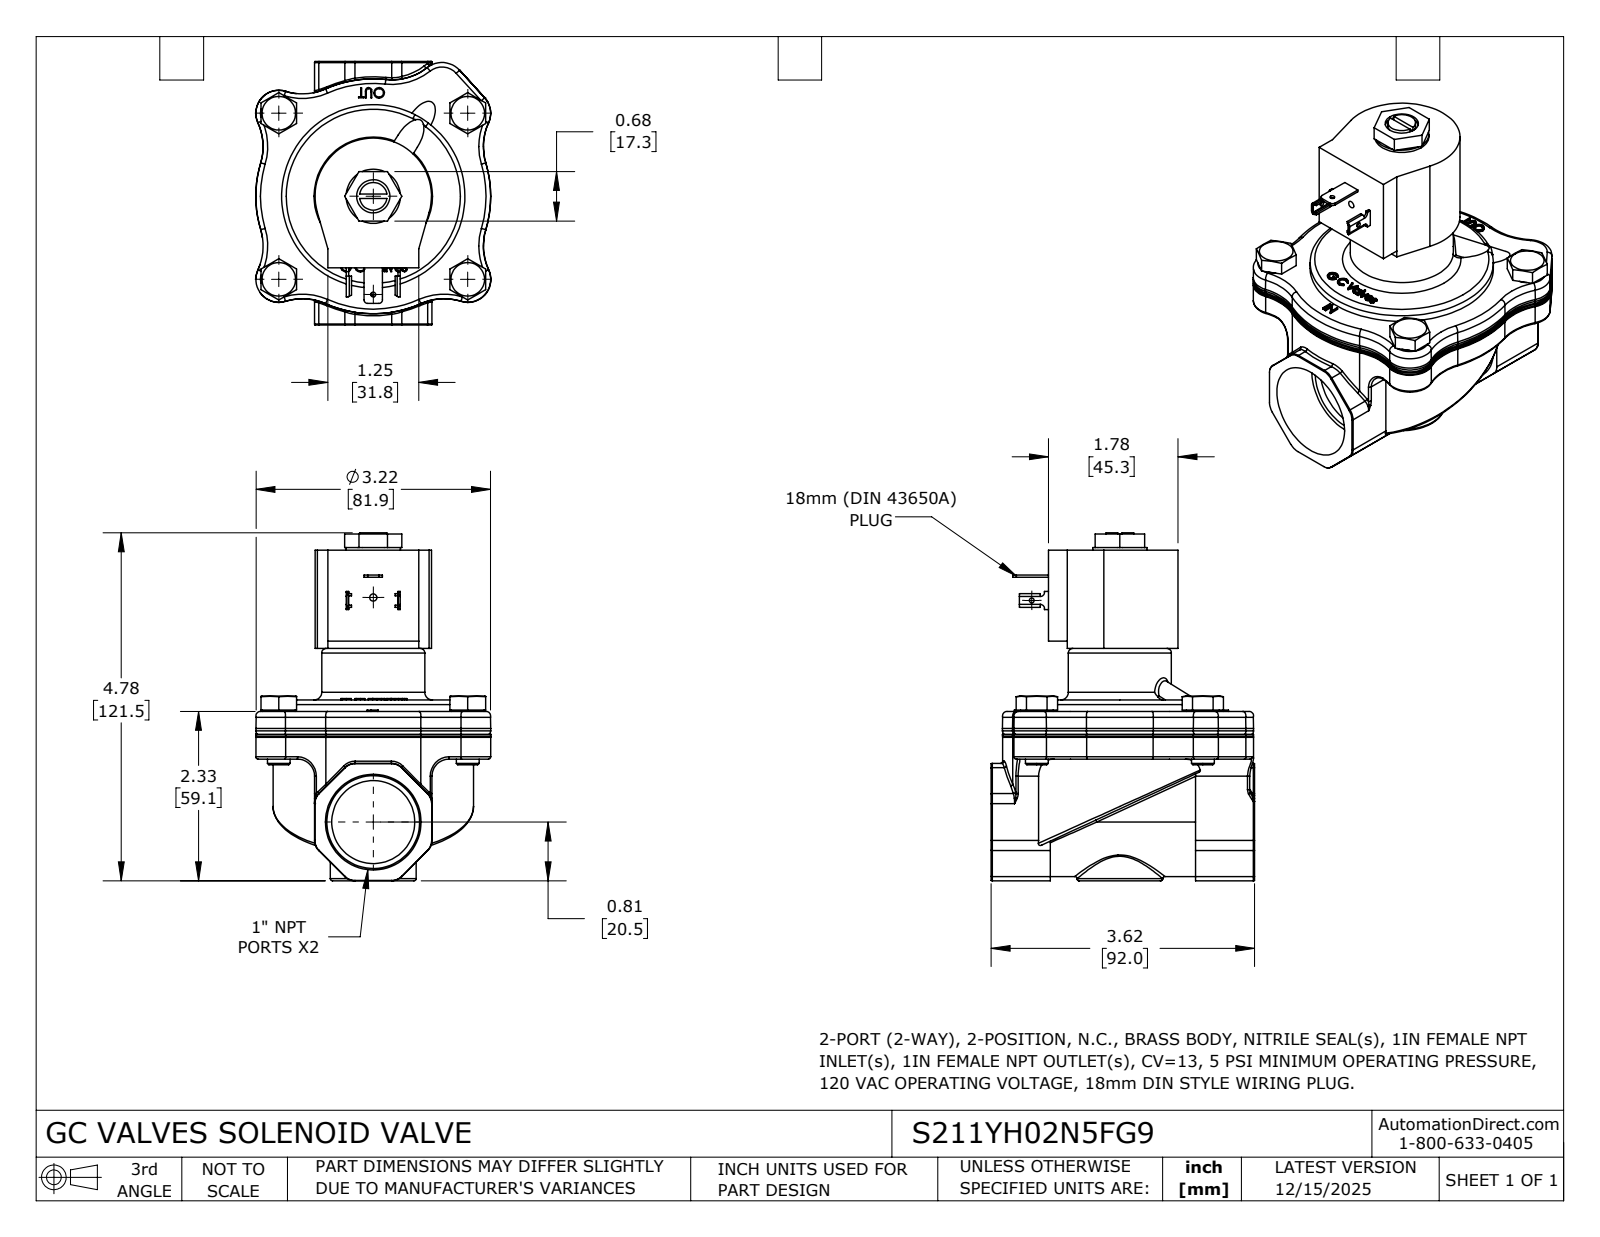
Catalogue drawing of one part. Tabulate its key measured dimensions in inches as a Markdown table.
| quantity | value |
| --- | --- |
| part name | S211YH02N5FG9 |
| STEP written by | SolidWorks 2024 (CONFIG_CONTROL_DESIGN) |
| units | inches |
| bodies | 1 solid, 691 faces (224 planar, 180 cylindrical, 287 other) |
| overall size | 4.782 × 3.622 × 3.232 |
| volume | 19.21 in³ |
| surface area | 67.88 in² |
| round holes (diameter × count) | 0.066 × 1, 0.067 × 1, 0.1 × 1, 0.456 × 1, 1.141 × 1 |
| round bosses / shafts (diameter × count) | 0.45 × 4, 0.313 × 4, 2.52 × 1, 1.417 × 1, 1.181 × 1, 0.746 × 1, 0.38 × 1 |
| partial cylindrical surfaces (radius × count) | 0.031 × 24, 0.787 × 24, 0.315 × 12, 0.197 × 8, 0.006 × 4, 0.041 × 4, 0.05 × 2, 0.06 × 2 |
| main face-to-face distances | 0.157, 2.216, 2.059, 2.328, 2.485, 4.544, 1.673, 0.655, 0.812, 2.871 |
| hole center spacings | 1.35, 3.086 |
